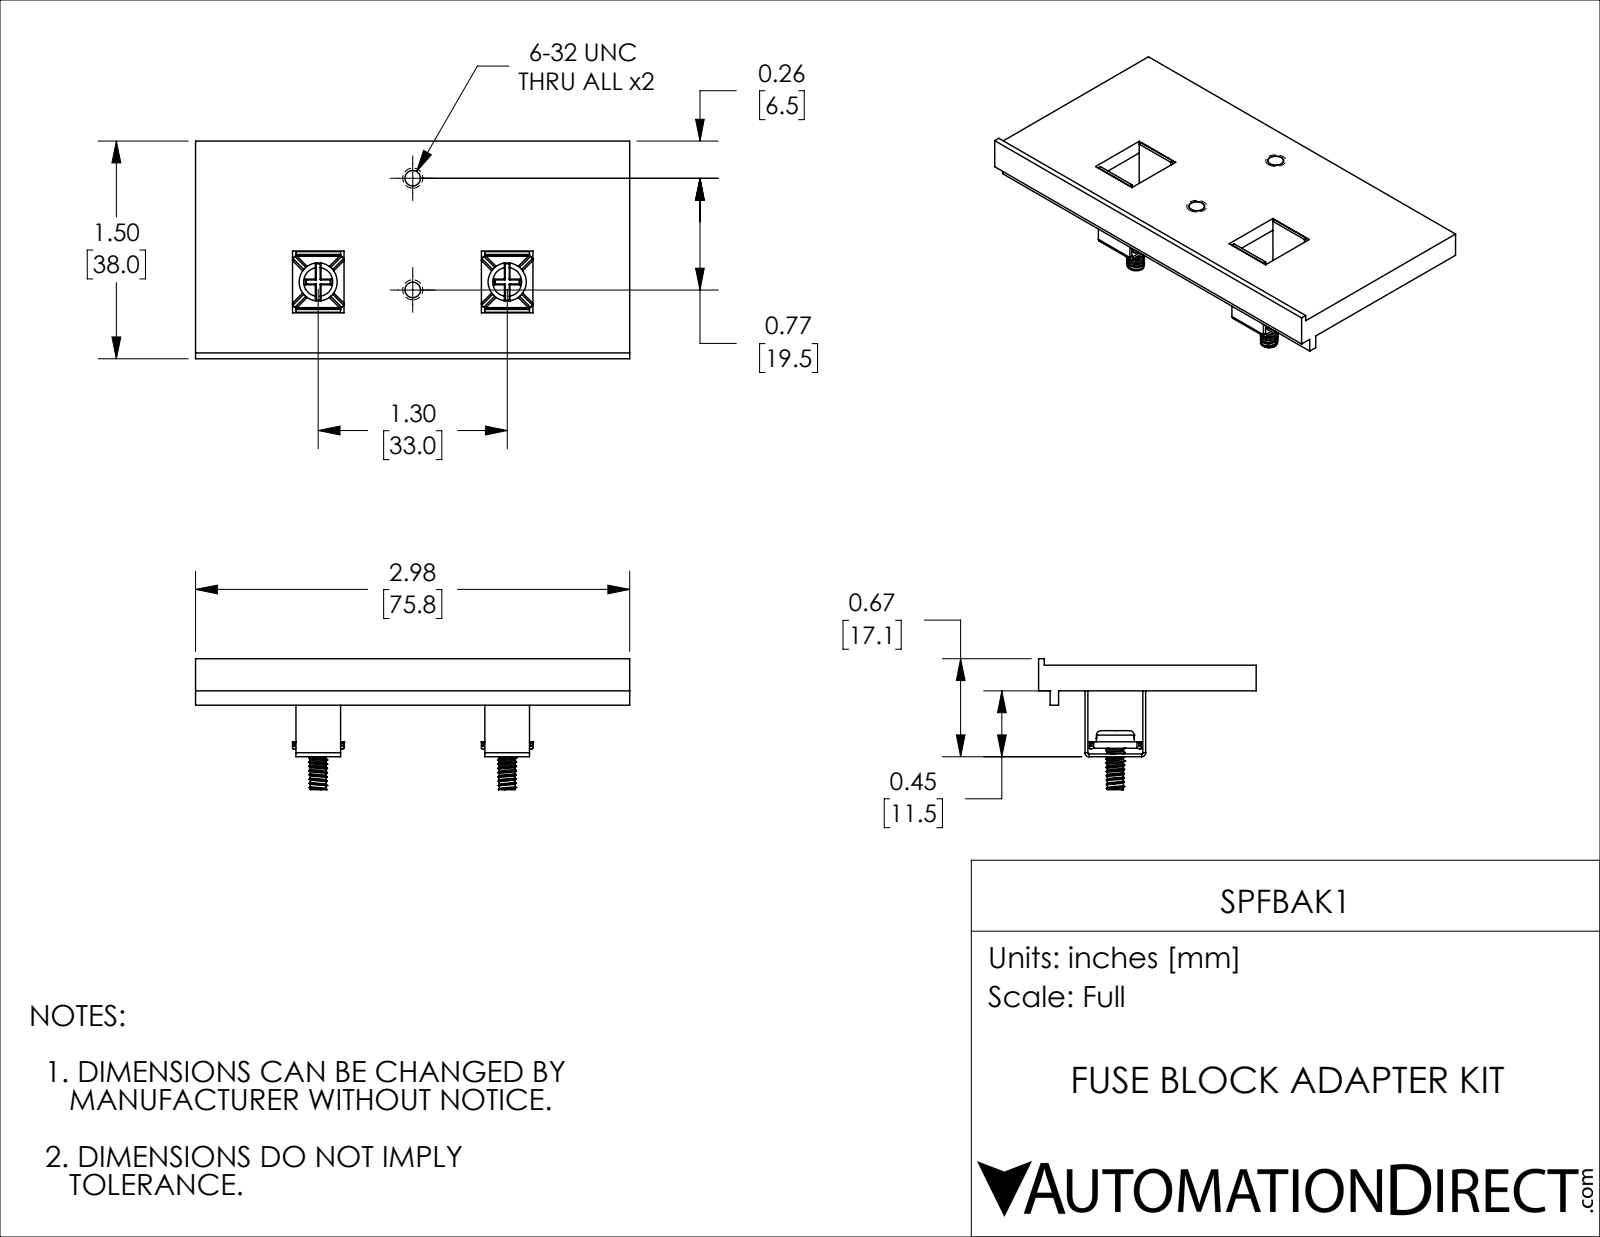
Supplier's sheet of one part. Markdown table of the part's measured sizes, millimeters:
| quantity | value |
| --- | --- |
| part name | SPFBAK1 |
| STEP written by | SolidWorks 2018 (AUTOMOTIVE_DESIGN) |
| units | millimeters |
| bodies | 7 solids, 344 faces (138 planar, 160 cylindrical, 46 other) |
| overall size | 75.8 × 38 × 22.84 |
| volume | 8 700 mm³ |
| surface area | 9 837 mm² |
| round holes (diameter × count) | 2.66 × 2, 2.71 × 2, 3.5 × 2 |
| round bosses / shafts (diameter × count) | 6.65 × 2, 2.79 × 2 |
| partial cylindrical surfaces (radius × count) | 0.13 × 18, 0.3 × 12, 0.74 × 8, 0.89 × 6, 0.2 × 2, 0.7 × 2 |
| main face-to-face distances | 2.5, 0.5, 1.5, 2, 4.5, 34.5, 10.1, 38, 3.5, 8.1 |
| hole center spacings | 16.56, 24.49, 19.5, 33 |
